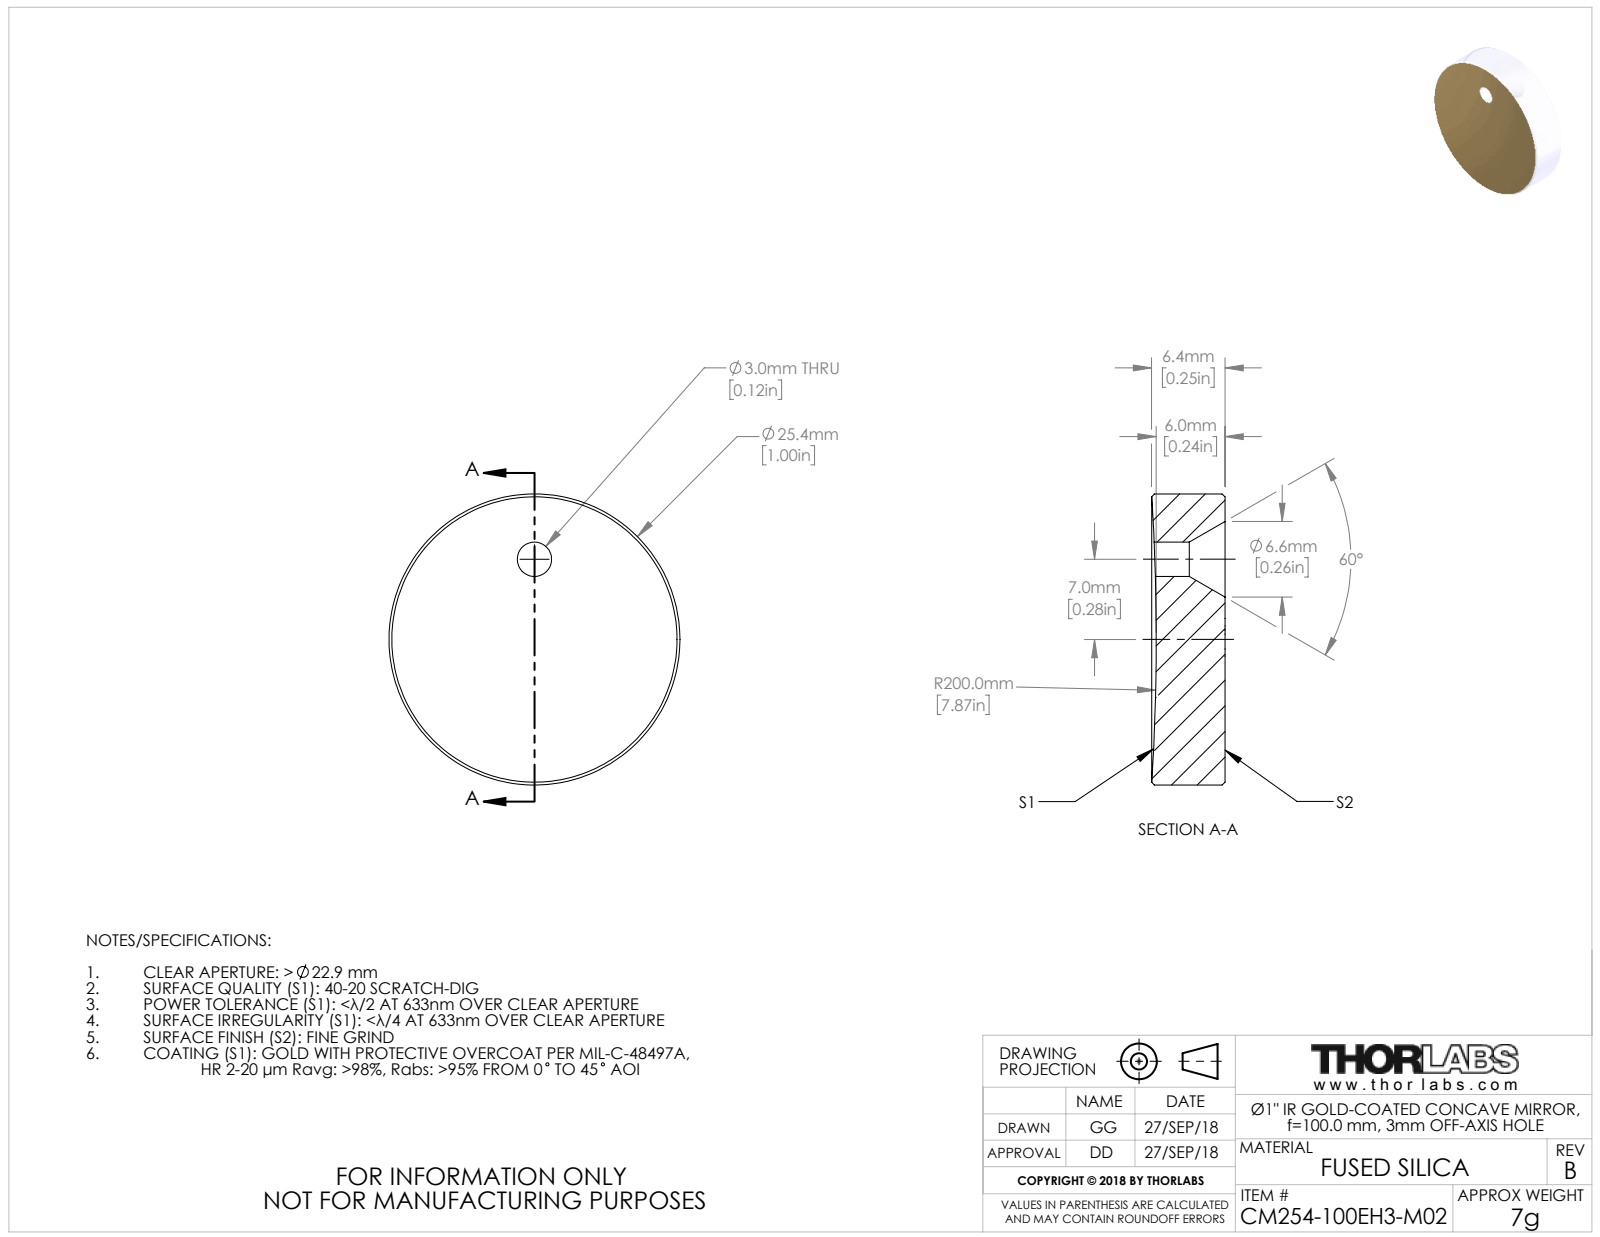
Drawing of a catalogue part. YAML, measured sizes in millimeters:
part_name: "TTN028024-E0W"
step_written_by: "SolidWorks 2014 (CONFIG_CONTROL_DESIGN)"
units: millimeters
bodies: {solids: 1, faces: 46, planar: 34, cylindrical: 4, other: 8}
overall_size: [25.4, 25.4, 6.4]
volume: 3060
surface_area: 1543
round_holes:
  - {diameter: 3, count: 1}
round_bosses_or_shafts:
  - {diameter: 25.4, count: 1}
